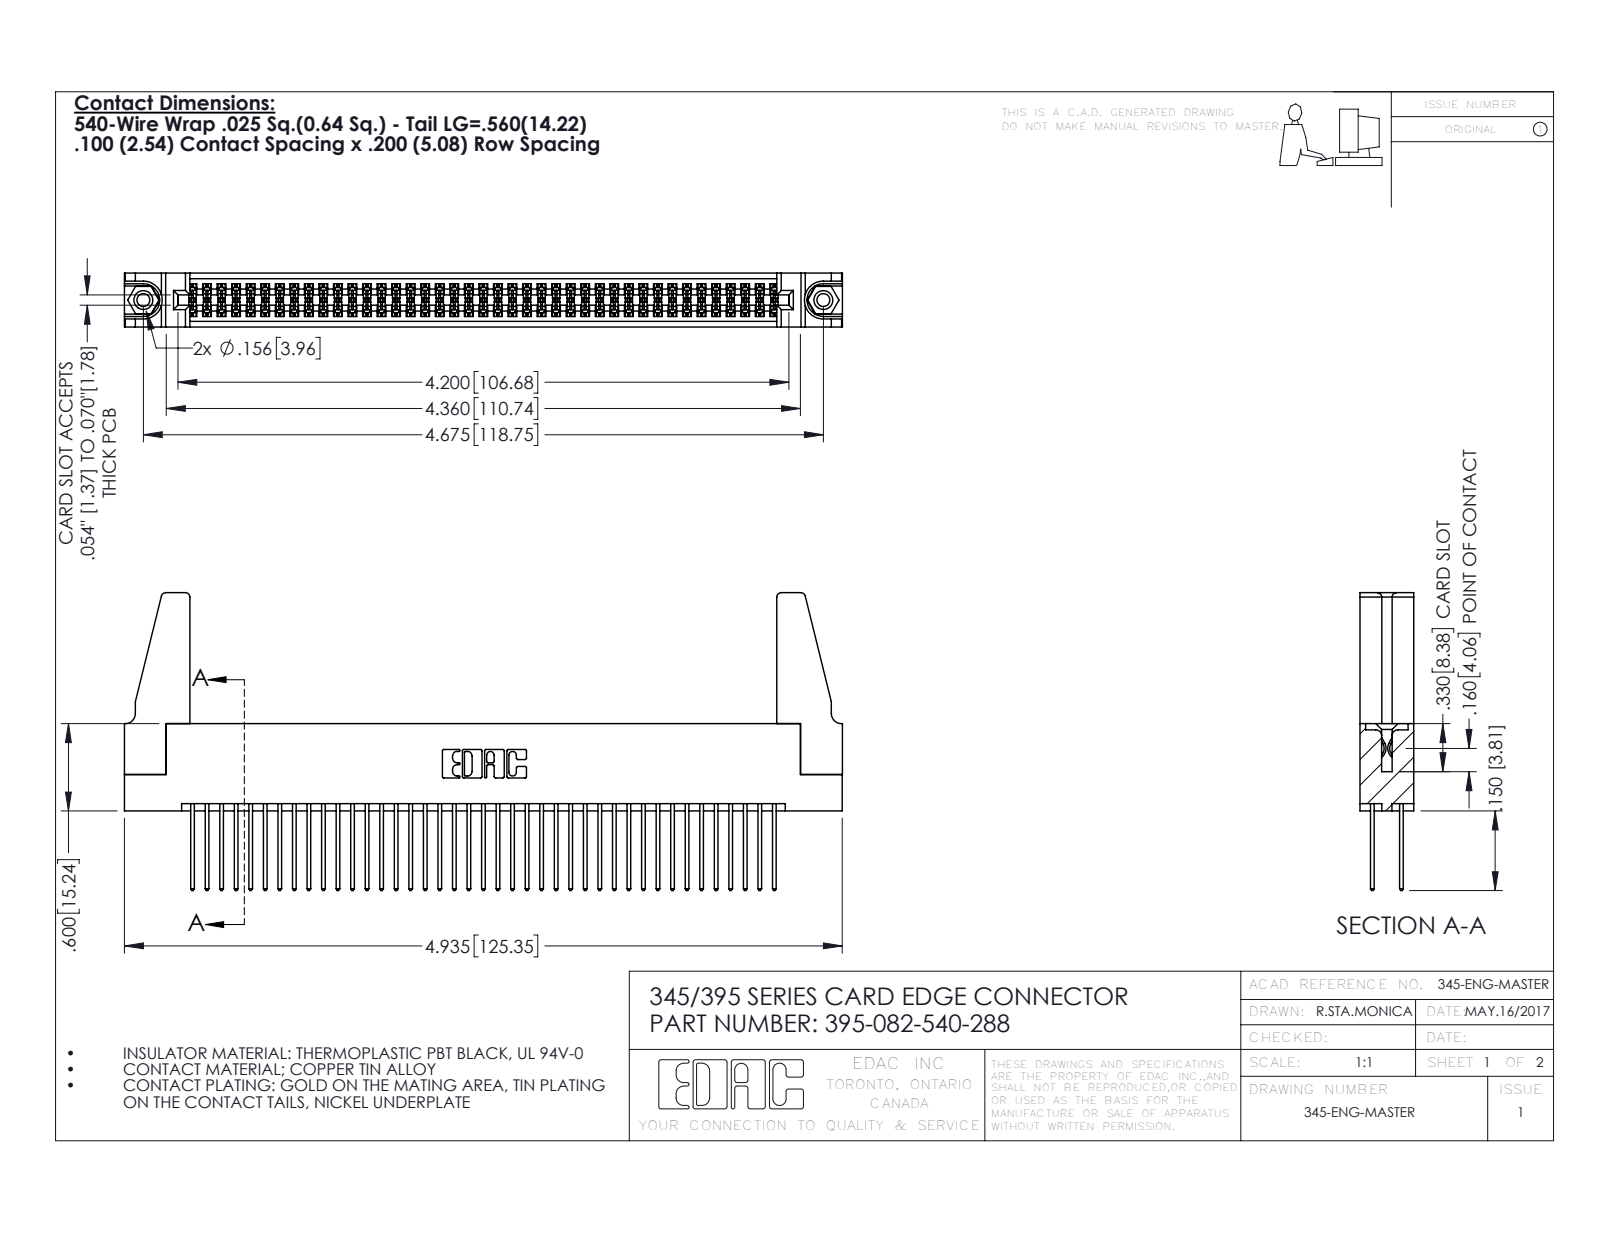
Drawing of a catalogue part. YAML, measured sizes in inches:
part_name: "345 Part_Flush Mounting Lugs - 0.156 Dia-TH; 345-292-001_345-293-140; 345-250-001_345-250-001-102; 345-220-078_345-220-088 (+1 more)"
step_written_by: "SolidWorks 2016 (CONFIG_CONTROL_DESIGN)"
units: inches
bodies: {solids: 87, faces: 4350, planar: 2858, cylindrical: 1476, other: 16}
overall_size: [4.936, 2.047, 0.37]
volume: 0.96
surface_area: 35.64
round_holes:
  - {diameter: 0.089, count: 2}
  - {diameter: 0.125, count: 2}
  - {diameter: 0.156, count: 2}
  - {diameter: 0.064, count: 1}
round_bosses_or_shafts:
  - {diameter: 0.155, count: 2}
partial_cylinders:
  - {radius: 0.006, count: 123}
  - {radius: 0.01, count: 82}
  - {radius: 0.01, count: 22}
  - {radius: 0.03, count: 8}
  - {radius: 0.007, count: 6}
  - {radius: 0.031, count: 6}
  - {radius: 0.026, count: 3}
  - {radius: 0.014, count: 2}
face_to_face_distances: [0.072, 0.298, 0.2, 0.098, 0.272, 0.025, 0.37, 0.225, 0.175, 0.149]
hole_center_spacings: [0.27, 4.439, 4.675]
